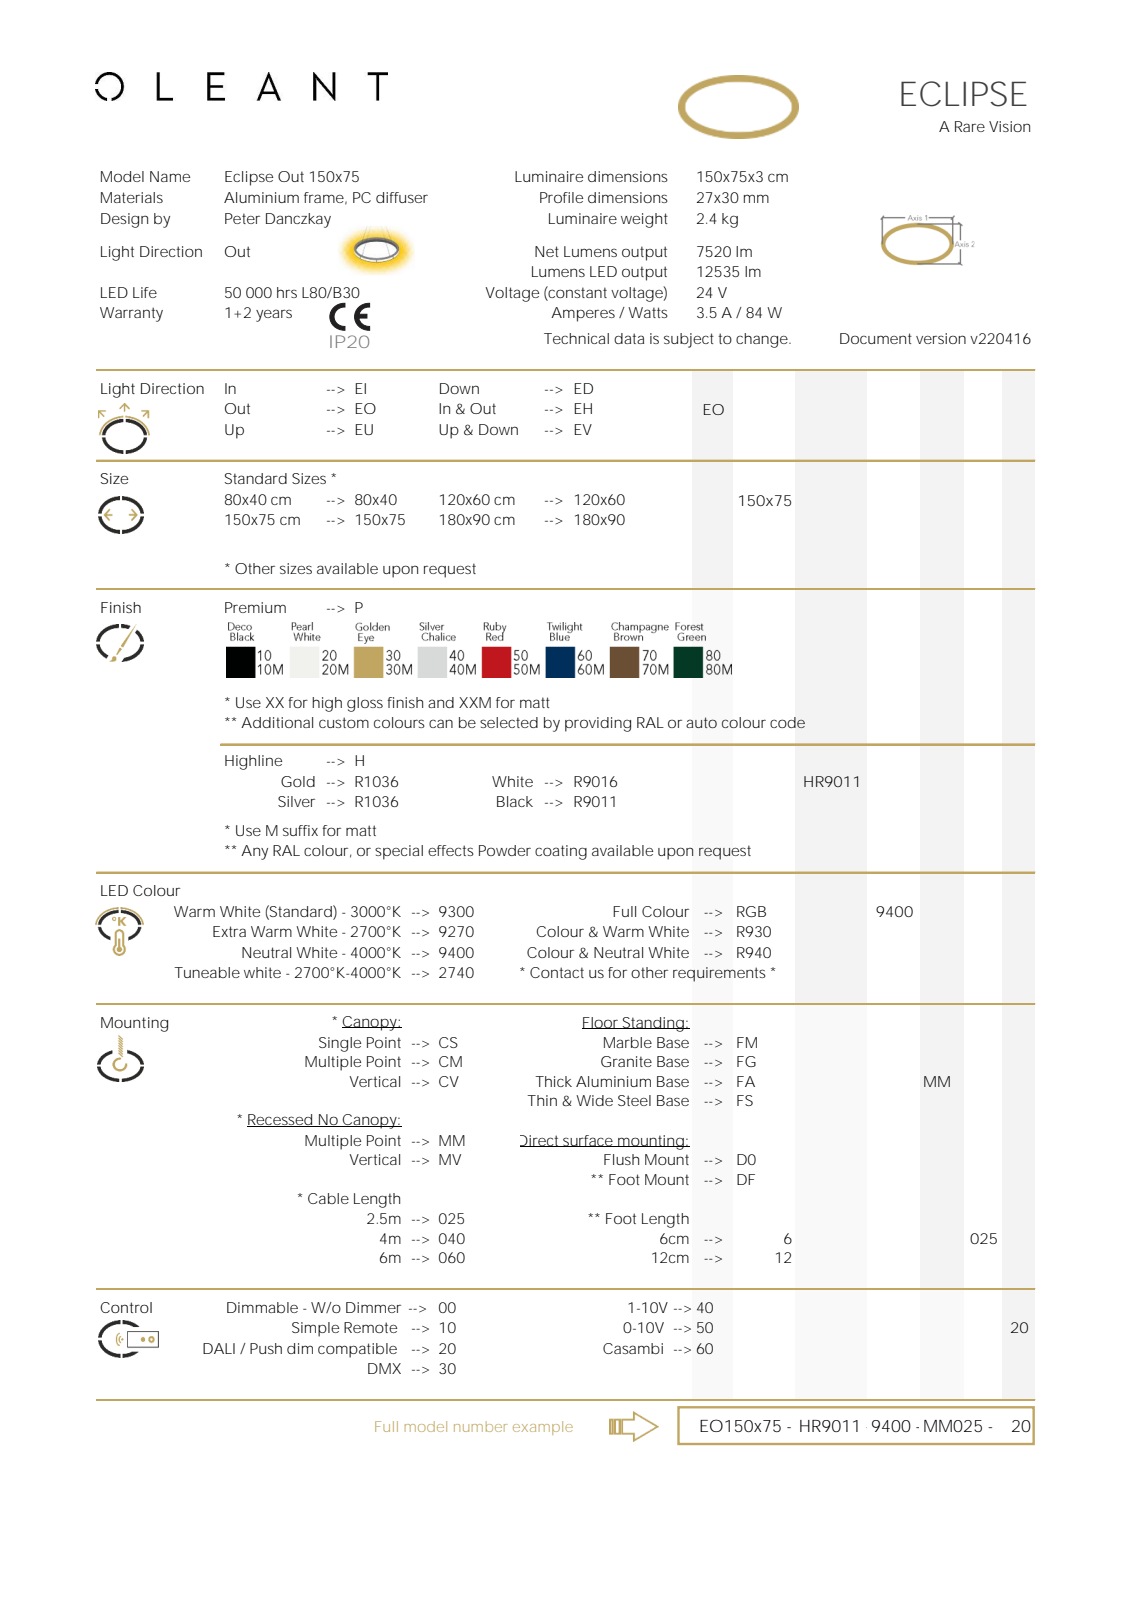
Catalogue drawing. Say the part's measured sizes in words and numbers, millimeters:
The part is named "eclipse; frame; plexi; cable (+1 more)". Its 3-D file was written by "Autodesk Inventor 2020 (AUTOMOTIVE_DESIGN)". It is 10 solids with 89 faces: 48 planar, 20 cylindrical and 21 other. Overall it measures 1500 by 1053 by 750 millimeters. Its volume is 2 437 000 cubic millimeters and its surface area 932 516 square millimeters. Round holes: 4 of diameter 3. Round bosses or shafts: 4 of diameter 11, 4 of diameter 9, 4 of diameter 4, 4 of diameter 1.2. The main face-to-face distances are 2, 28, 26, 30, 12.01, 707.89, 719.9, 695.88, 1053, 1051. The hole center spacings are 511.52, 1038.94, 1158.04.
